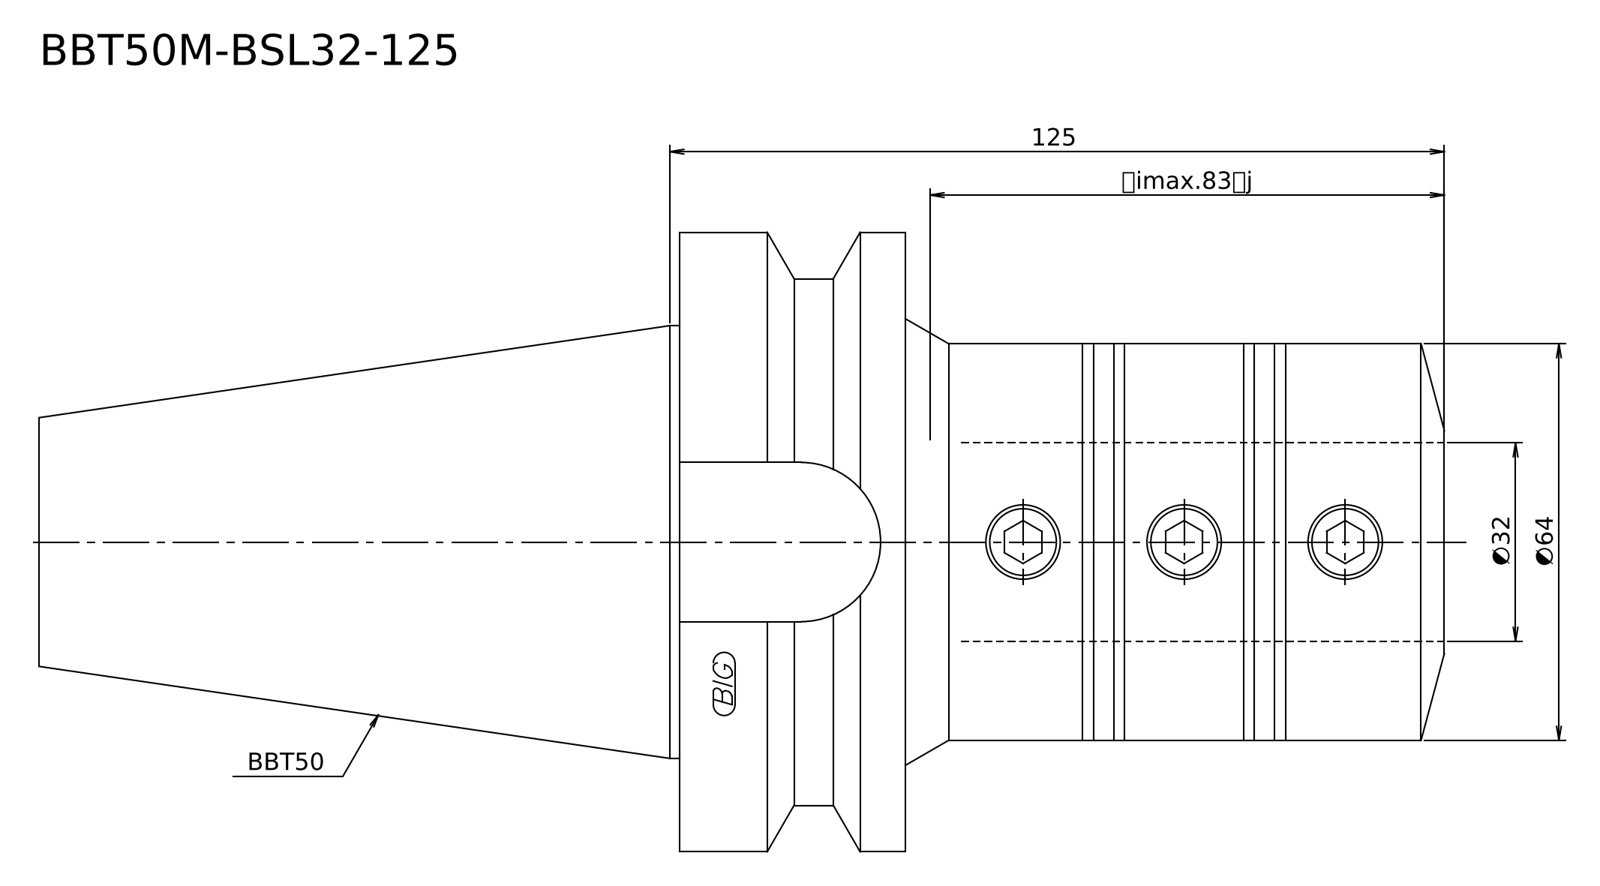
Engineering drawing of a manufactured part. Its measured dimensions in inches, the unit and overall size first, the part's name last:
Units: inches
Overall size (bounding box): 8.929 × 3.937 × 3.937
Round bosses / shafts (diameter × count): ⌀3.937 ×1, ⌀3.346 ×1, ⌀2.75 ×1, ⌀2.52 ×1
Main face-to-face distances: 1.437, 5.504, 4.067, 3.425, 4.862, 8.929
Volume: 48.51 in³ · Surface area: 94.55 in²
Bodies: 1 solid, 14 faces (4 planar, 5 cylindrical, 5 other)
STEP written by: Kubotek KeyCreator V8.5.1 (14335) (CONFIG_CONTROL_DESIGN)
